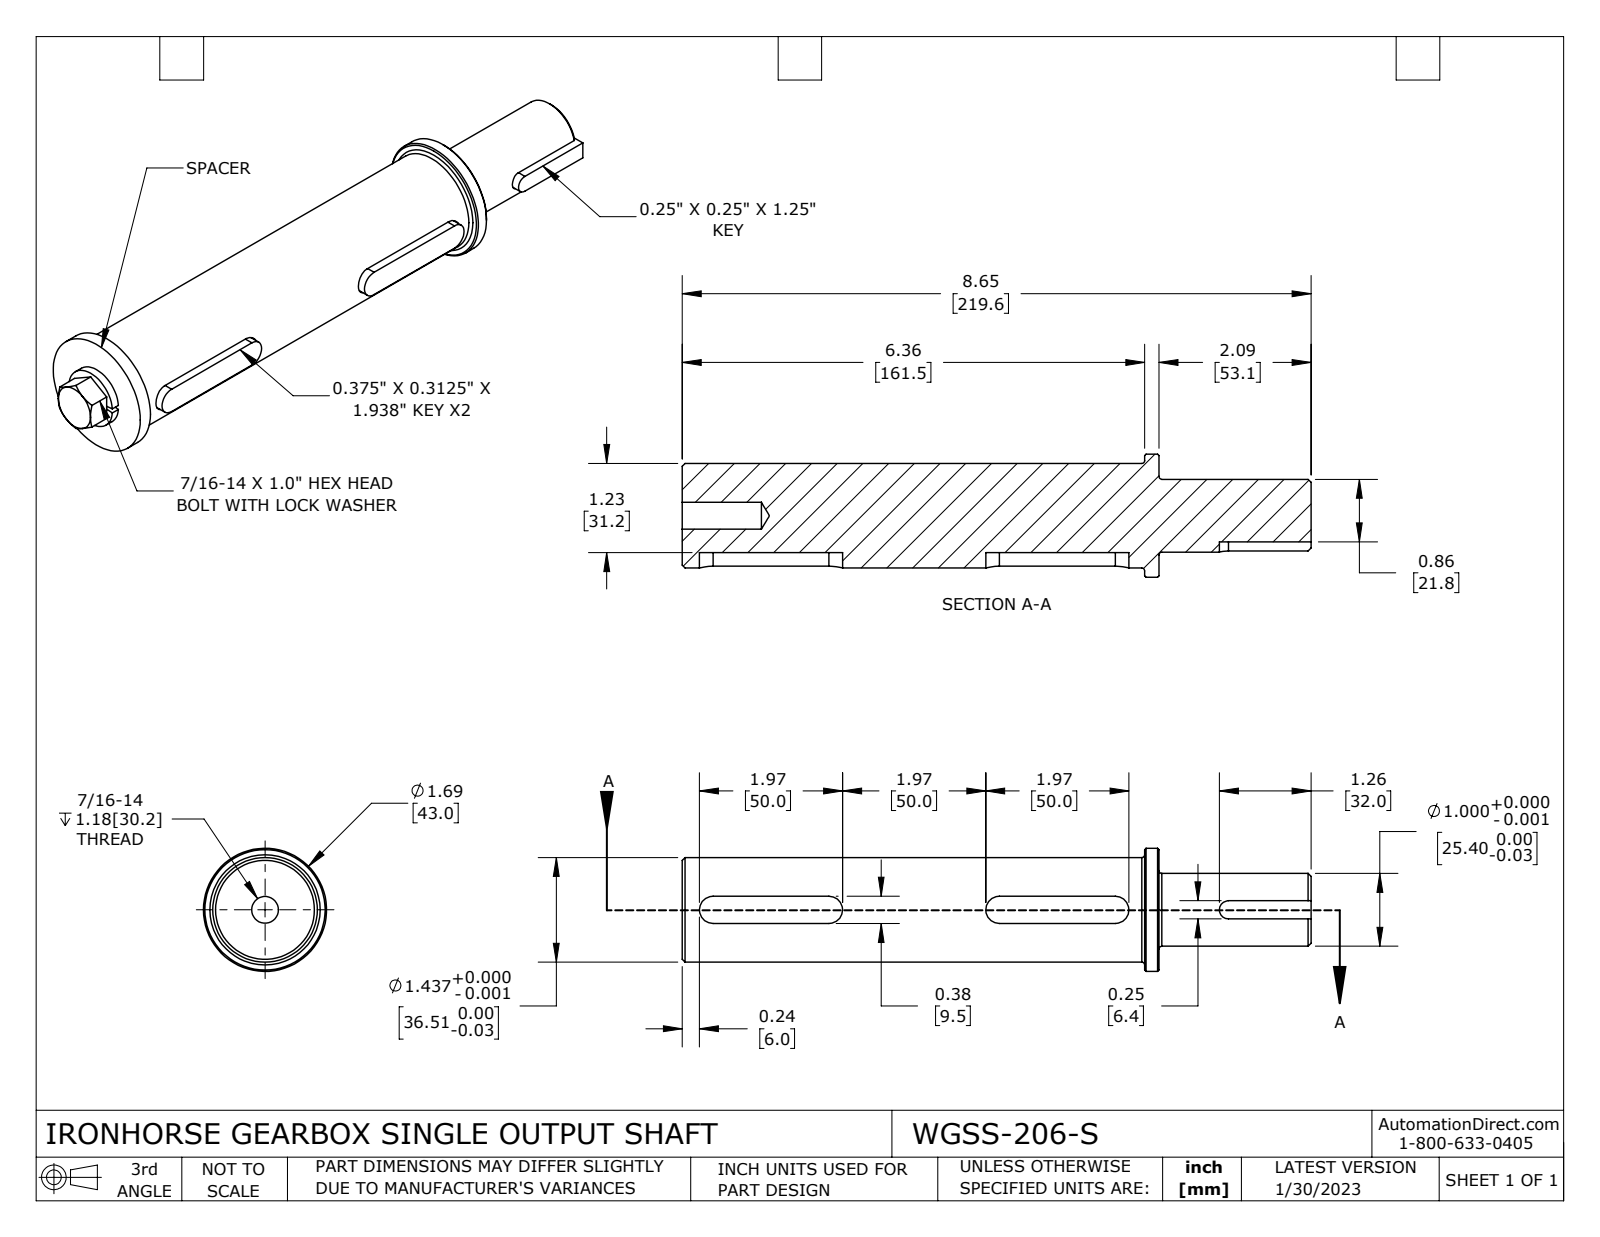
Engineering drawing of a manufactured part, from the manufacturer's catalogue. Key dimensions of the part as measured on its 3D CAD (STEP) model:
Part name (STEP PRODUCT): WGSS-206-S
STEP written by: SolidWorks 2021 (CONFIG_CONTROL_DESIGN)
Units: inches
Bodies: 7 solids, 95 faces (41 planar, 31 cylindrical, 23 other)
Overall size (bounding box): 9.276 × 1.693 × 1.693
Volume: 13.17 in³ · Surface area: 59.86 in²
Round holes (diameter × count): ⌀0.368 ×1, ⌀0.472 ×1, ⌀0.48 ×1
Round bosses / shafts (diameter × count): ⌀1.693 ×1, ⌀1.437 ×1, ⌀1 ×1, ⌀0.846 ×1, ⌀0.437 ×1
Partial cylindrical surfaces — rounded edges, fillets, slot ends (radius × count): R0.188 ×4, R0.188 ×3, R0.125 ×2, R0.187 ×1
Main face-to-face distances: 0.197, 0.313, 6.555, 6.752, 0.375, 8.842, 8.645, 2.09, 0.062, 0.149
